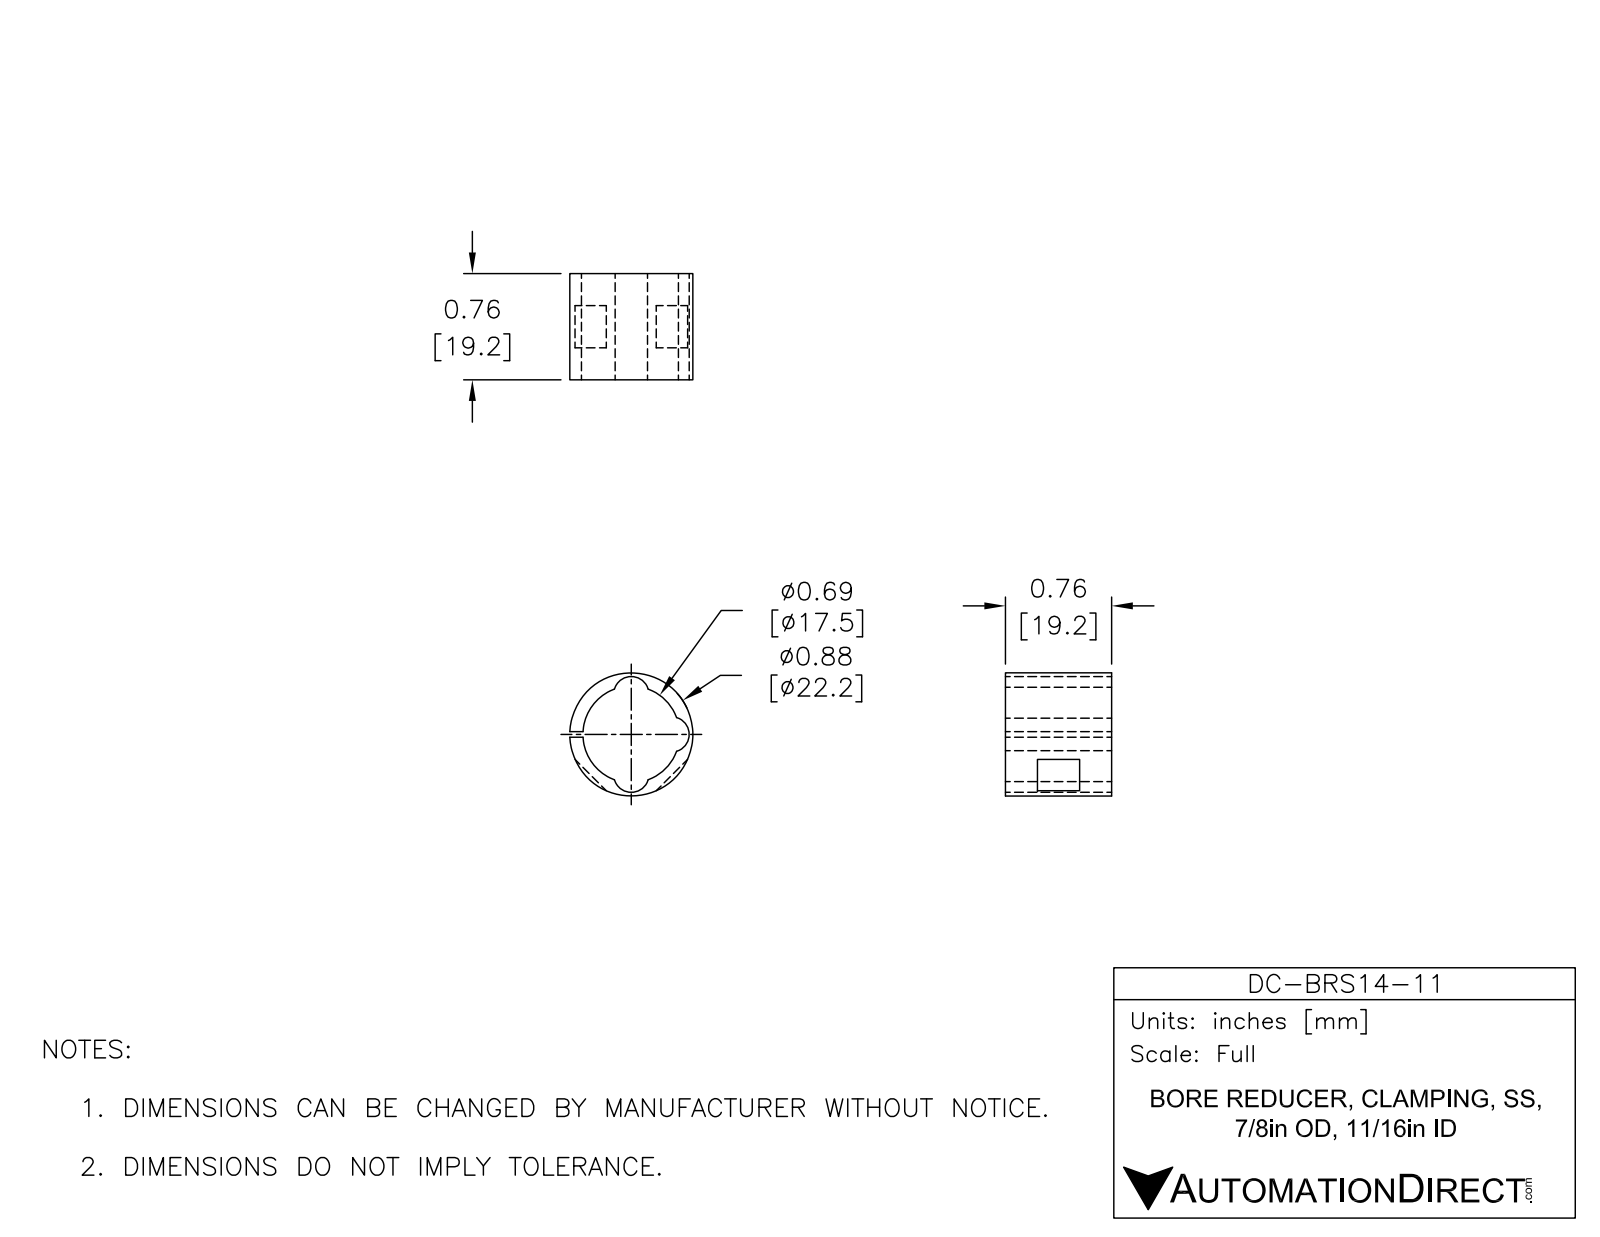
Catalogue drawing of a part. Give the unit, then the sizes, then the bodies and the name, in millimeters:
Units: millimetres
Overall size (bounding box): 22.23 × 22.21 × 19.18
Round bosses / shafts (diameter × count): ⌀22.22 ×1
Partial cylindrical surfaces — rounded edges, fillets, slot ends (radius × count): R3.17 ×3, R8.73 ×1
Main face-to-face distances: 19.18, 1.02, 5.78, 13.4, 7.62
Volume: 2 285 mm³ · Surface area: 2 811 mm²
Bodies: 1 solid, 21 faces (10 planar, 11 cylindrical, 0 other)
Part name (STEP PRODUCT): DC-BRS14-11
STEP written by: SolidWorks 2015 (AUTOMOTIVE_DESIGN)
